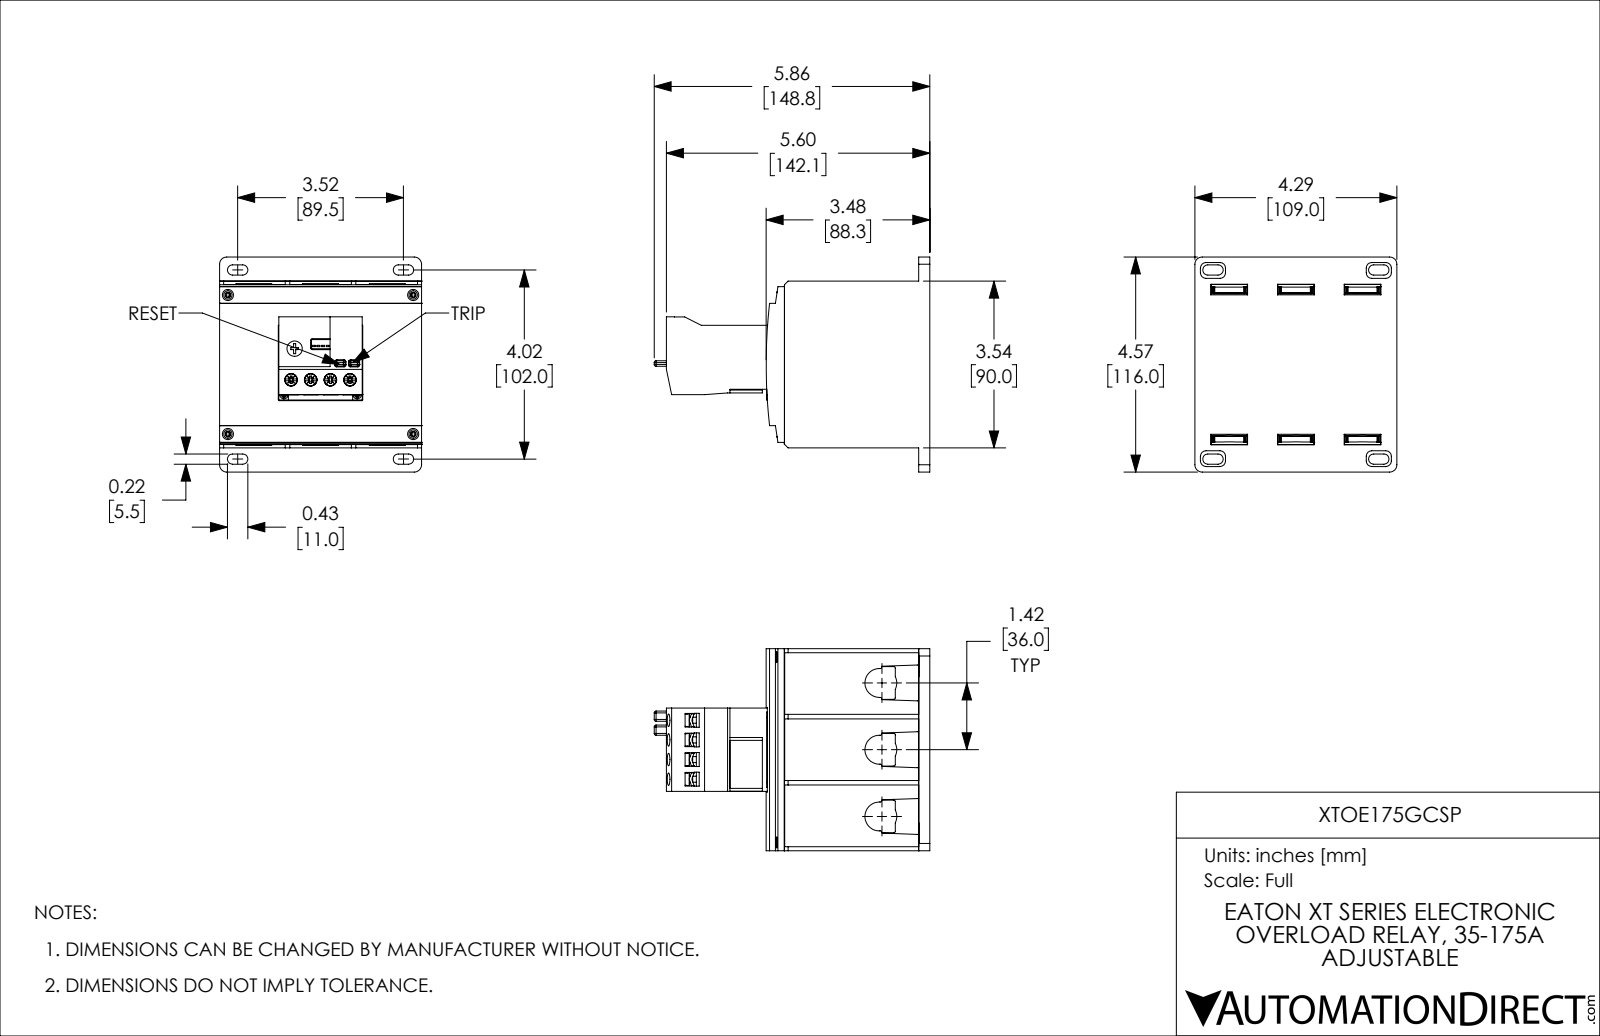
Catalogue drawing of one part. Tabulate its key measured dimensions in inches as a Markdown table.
| quantity | value |
| --- | --- |
| part name | XTOE175GCSP |
| STEP written by | SolidWorks 2018 (AUTOMOTIVE_DESIGN) |
| units | inches |
| bodies | 25 solids, 1031 faces (665 planar, 188 cylindrical, 178 other) |
| overall size | 5.856 × 4.567 × 4.291 |
| volume | 50.34 in³ |
| surface area | 182.6 in² |
| round holes (diameter × count) | 0.11 × 4, 0.14 × 4, 0.236 × 4, 0.268 × 4, 0.086 × 2, 0.126 × 2 |
| round bosses / shafts (diameter × count) | 0.177 × 6, 0.134 × 4, 0.128 × 4, 0.11 × 4, 0.098 × 4, 0.326 × 1 |
| partial cylindrical surfaces (radius × count) | 0.02 × 33, 0.039 × 14, 0.079 × 8, 0.108 × 8, 0.031 × 6, 0.154 × 4, 0.307 × 3, 0.315 × 3 |
| main face-to-face distances | 3.09, 4.291, 1.26, 3.031, 2.854, 0.235, 1.772, 0.732, 0.497, 2.357 |
| hole center spacings | 0.417, 0.835, 0.35, 0.417, 0.418, 1.769, 2.518, 3.158 |
